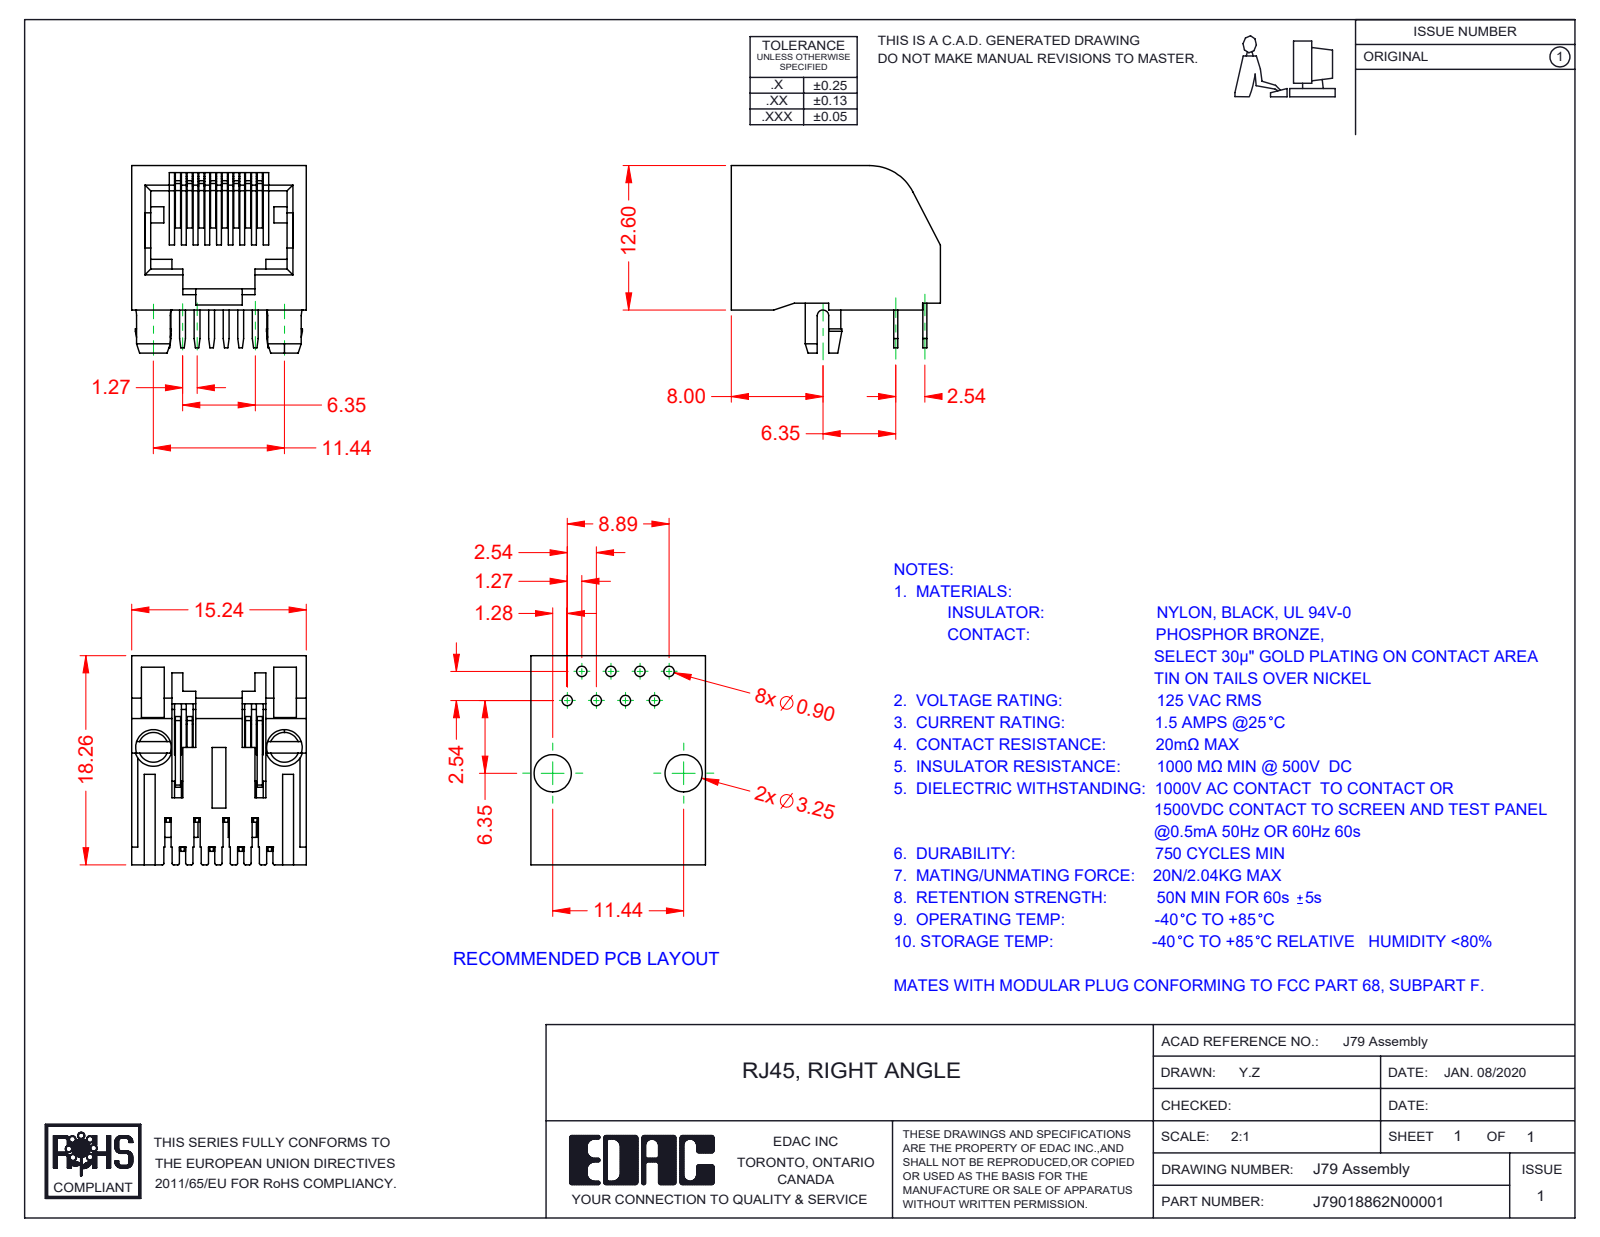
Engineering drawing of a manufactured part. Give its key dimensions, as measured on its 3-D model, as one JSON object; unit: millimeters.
{"part_name": "RJ79018862N00001; 79 Contacts; 79 Insulator", "step_written_by": "SolidWorks 2016 (CONFIG_CONTROL_DESIGN)", "units": "millimeters", "bodies": {"solids": 9, "faces": 574, "planar": 424, "cylindrical": 144, "other": 6}, "overall_size": [18.26, 16.36, 15.24], "volume_mm3": 1496, "surface_area_mm2": 3263, "round_bosses_or_shafts": [[3.1, 2]], "partial_cylinders_radius": [[0.15, 16], [0.5, 7], [0.72, 3], [0.36, 2], [1.65, 2], [1.8, 2], [2.16, 2], [0.2, 1]], "face_to_face_distances": [15.24, 2.04, 0.6, 12, 0.36, 4.08, 1.25, 9.8, 2.2, 8.2]}
